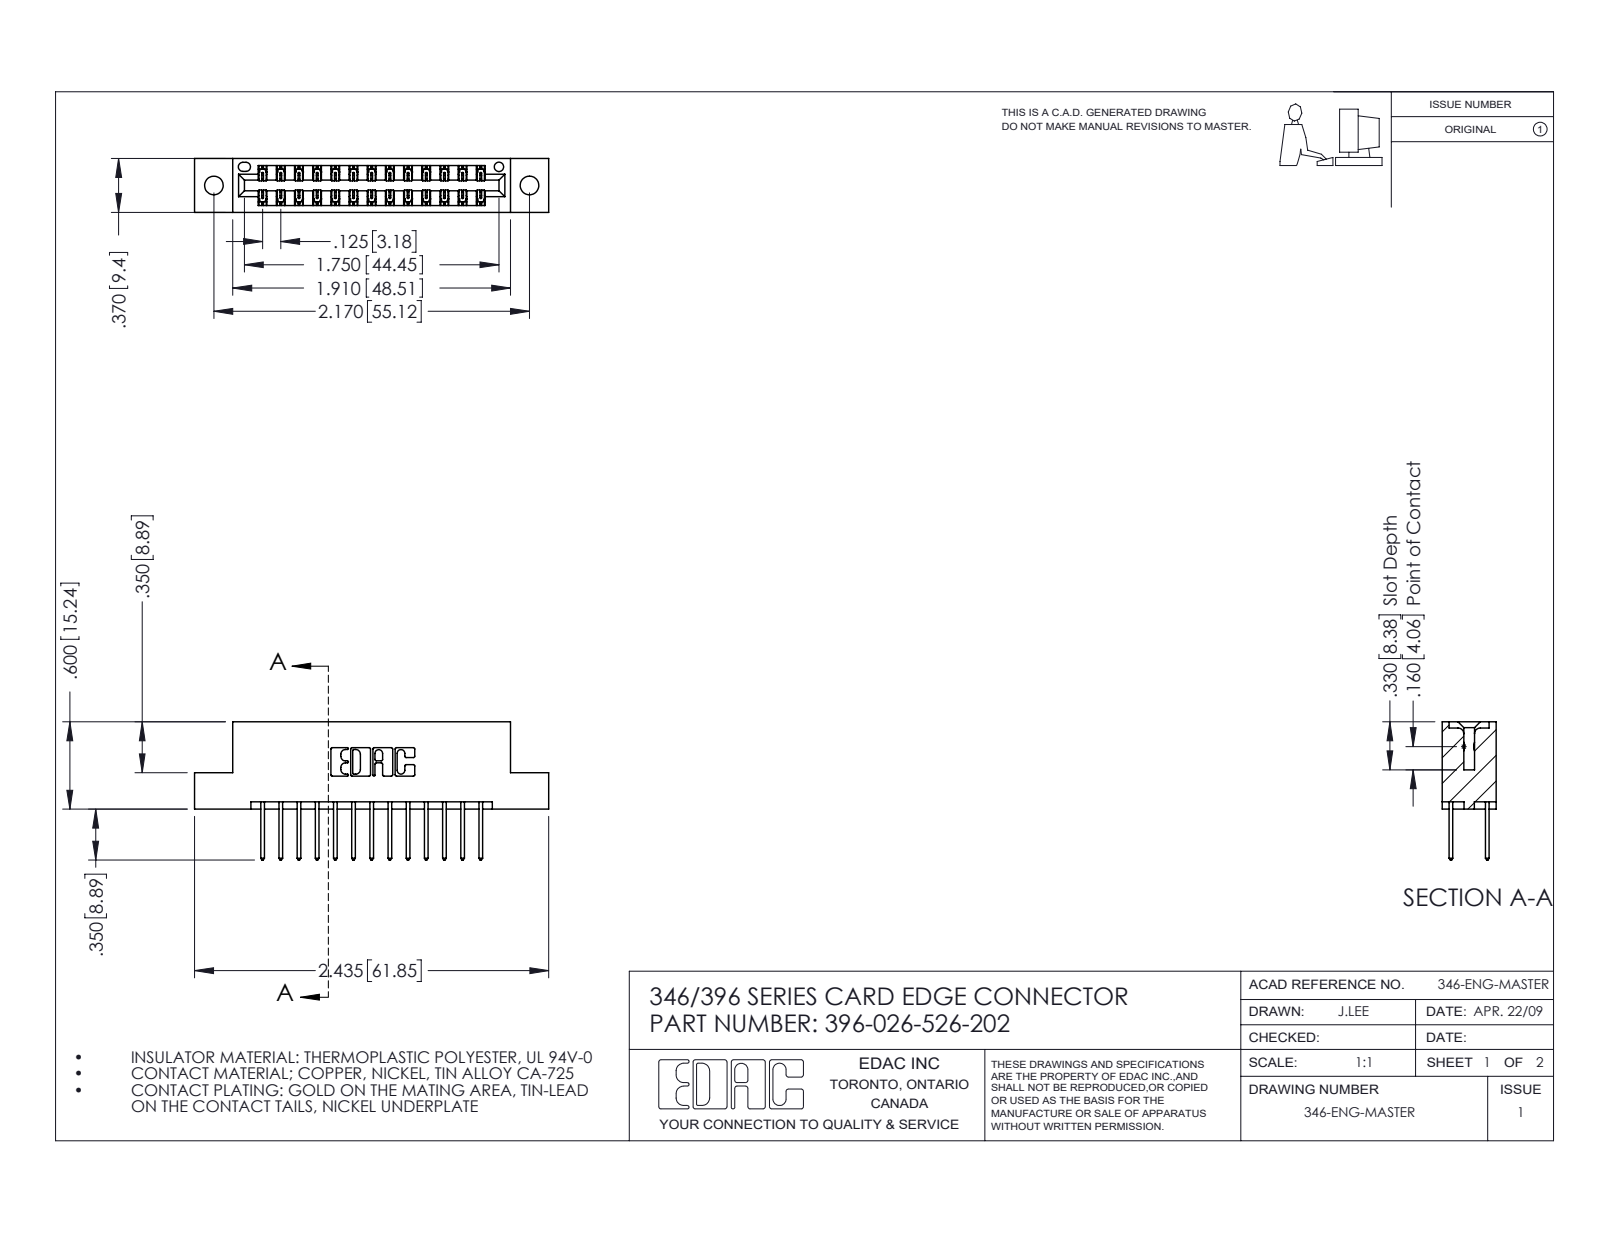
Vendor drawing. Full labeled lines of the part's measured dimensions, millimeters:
Part name (STEP PRODUCT): 345-292-001_345-293-126; 346 Part_Flush Mounting Lugs - 0.128 Dia; 396-026-526-202
STEP written by: SolidWorks 2016 (CONFIG_CONTROL_DESIGN)
Units: millimetres
Bodies: 27 solids, 1474 faces (986 planar, 488 cylindrical, 0 other)
Overall size (bounding box): 61.8 × 24.1 × 9.4
Volume: 5 820 mm³ · Surface area: 7 452 mm²
Round holes (diameter × count): ⌀3.3 ×2, ⌀1.6 ×1
Partial cylindrical surfaces — rounded edges, fillets, slot ends (radius × count): R0.2 ×39, R0.3 ×26, R0.3 ×22, R0.2 ×6, R0.8 ×6, R0.7 ×3, R0.4 ×2, R0.6 ×2
Main face-to-face distances: 6.4, 1.2, 8.2, 9.4, 1.8, 7.6, 0.6, 7, 3.8, 5.6
Hole centre spacings: 6.2, 49.9, 55.1
